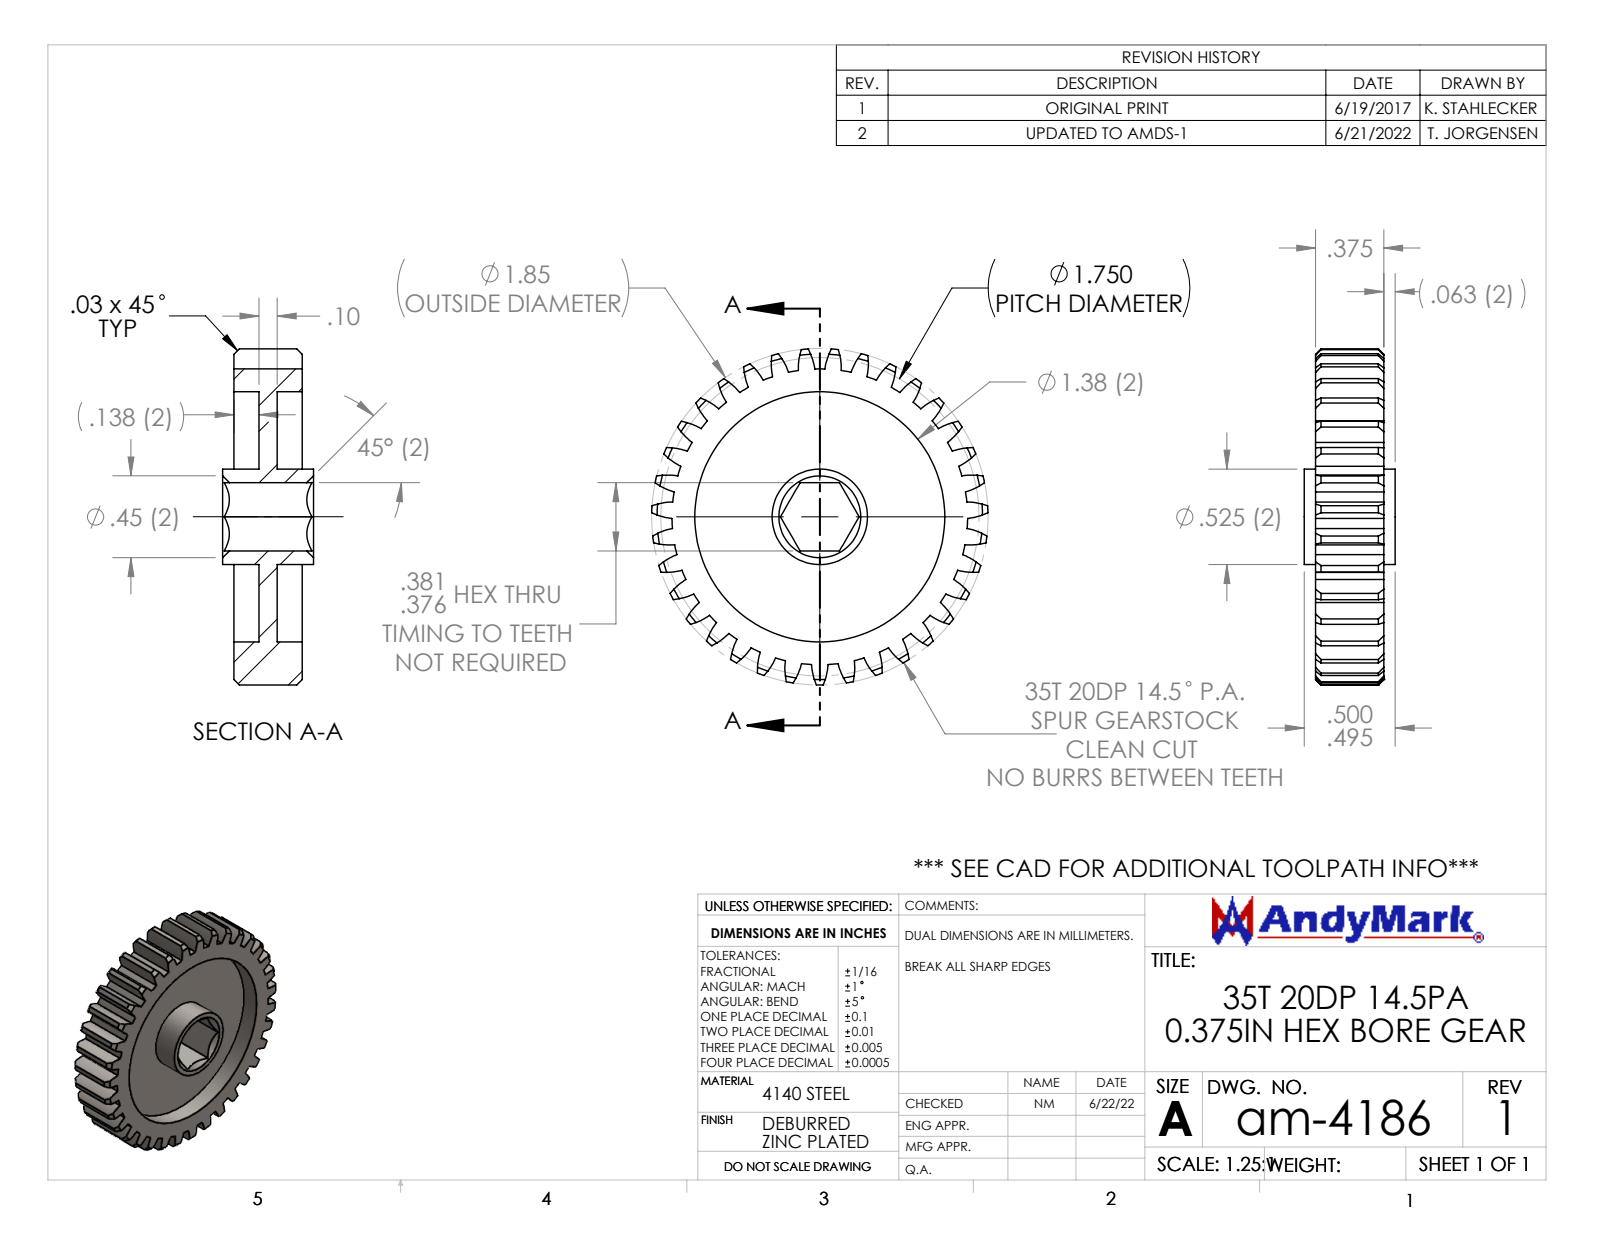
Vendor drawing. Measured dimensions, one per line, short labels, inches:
name: am-4186 35T 20DP 375hex 375 FW
written by: SolidWorks 2021 (CONFIG_CONTROL_DESIGN)
unit: in
bodies: 1 solid, 238 faces (12 planar, 152 cylindrical, 74 other)
size: 1.849 × 1.848 × 0.5
volume: 0.498 in³; area: 11.11 in²
holes: 1× ⌀1.375
bosses: 1× ⌀0.525
rounds: 70× R0.35, 1× R0.813, 1× R0.925
face distances: 0.1, 0.137, 0.237, 0.375, 0.238, 0.138, 0.375, 0.2, 0.3, 0.063
